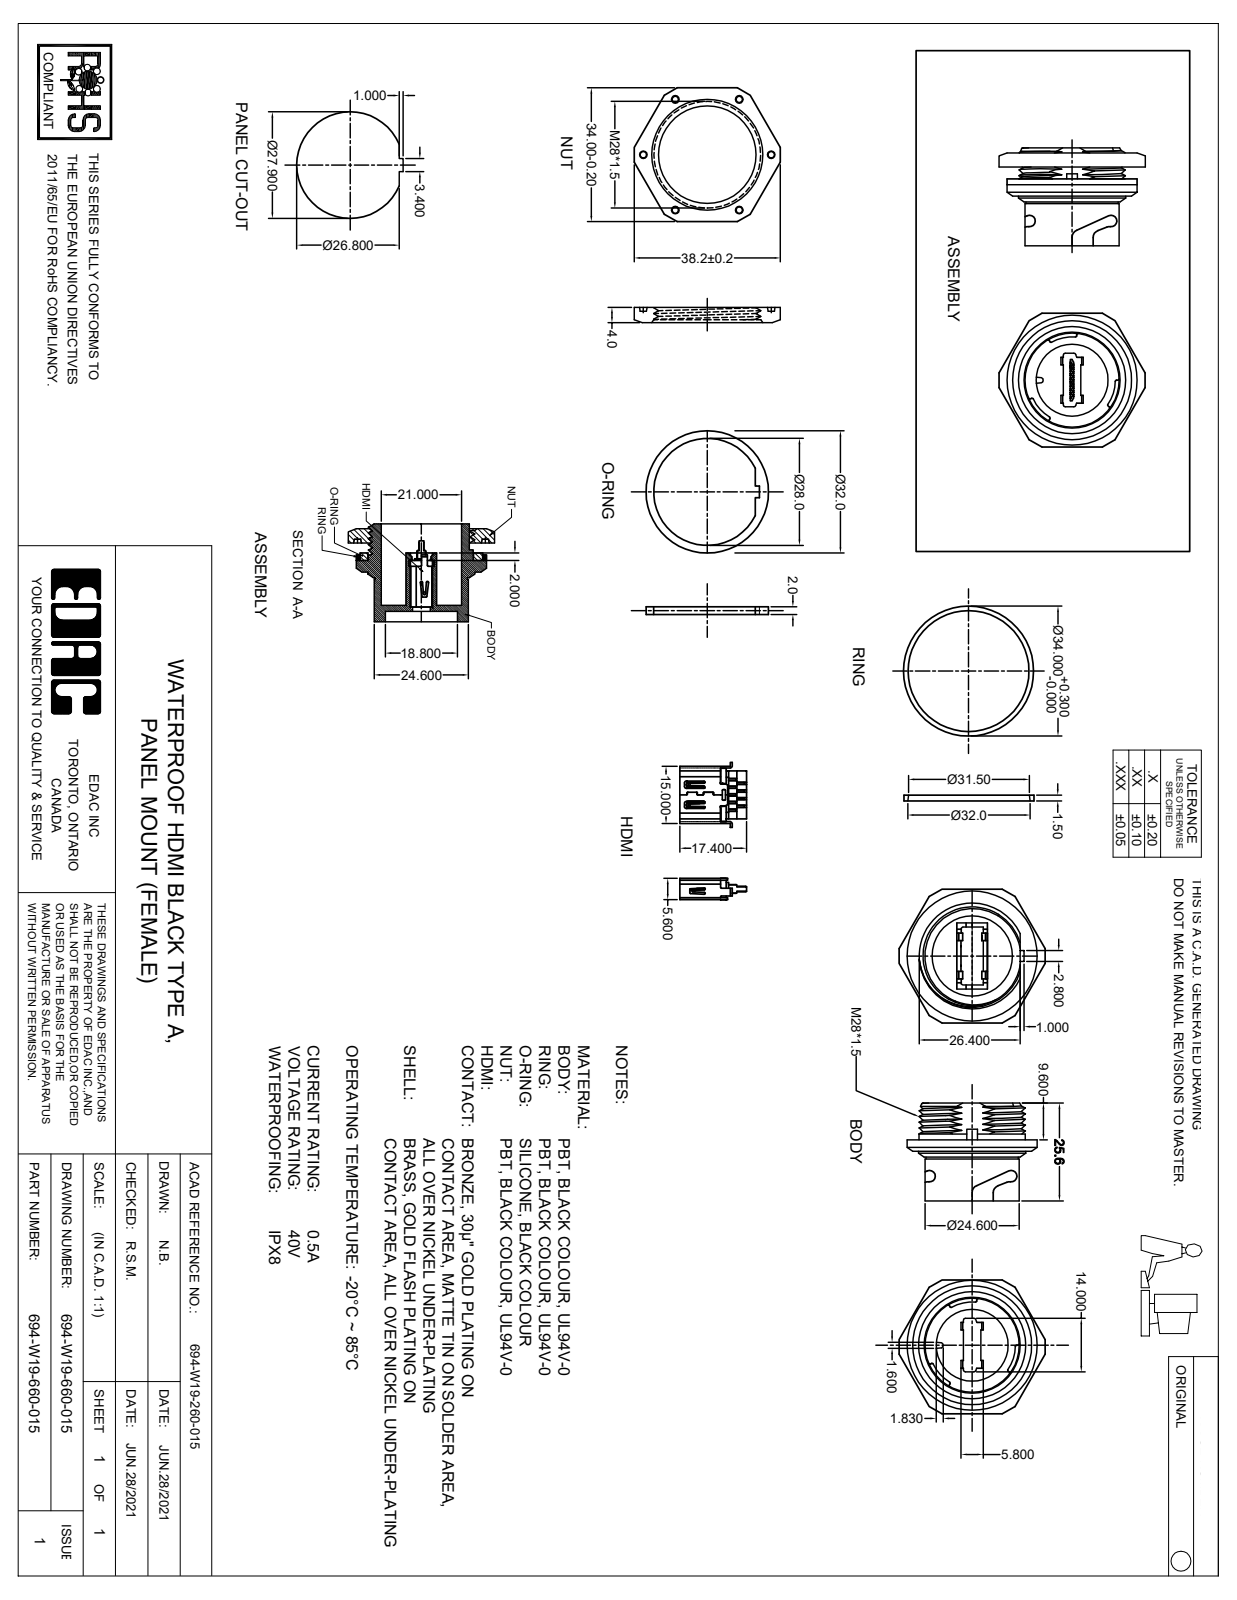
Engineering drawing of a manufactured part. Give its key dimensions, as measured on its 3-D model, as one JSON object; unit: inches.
{"part_name": "HDMI CONTACT2 694-W19-X60-015; HDMI ASSY 694-W19-X60-015; O-RING 694-W19-X60-015; HDMI HOUSING2 694-W19-X60-015 (+7 more)", "step_written_by": "SolidWorks 2020 (AUTOMOTIVE_DESIGN)", "units": "inches", "bodies": {"solids": 26, "faces": 2027, "planar": 1388, "cylindrical": 574, "other": 65}, "overall_size": [1.504, 1.369, 1.008], "volume_in3": 0.583, "surface_area_in2": 20.12, "round_holes": [[0.079, 6], [0.74, 1], [0.827, 1], [1.033, 1], [1.102, 1]], "round_bosses_or_shafts": [[1.339, 1], [1.26, 1], [1.094, 1], [0.969, 1], [0.949, 1]], "partial_cylinders_radius": [[0.006, 240], [0.008, 38], [0.008, 28], [0.02, 12], [0.01, 10], [0.004, 6], [0.014, 6], [0.026, 6]], "face_to_face_distances": [0.02, 0.157, 0.194, 0.043, 0.106, 0.352, 0.079, 0.273, 0.378, 0.224], "hole_center_spacings": [0.65, 1.125, 1.299, 0.65, 1.3]}
